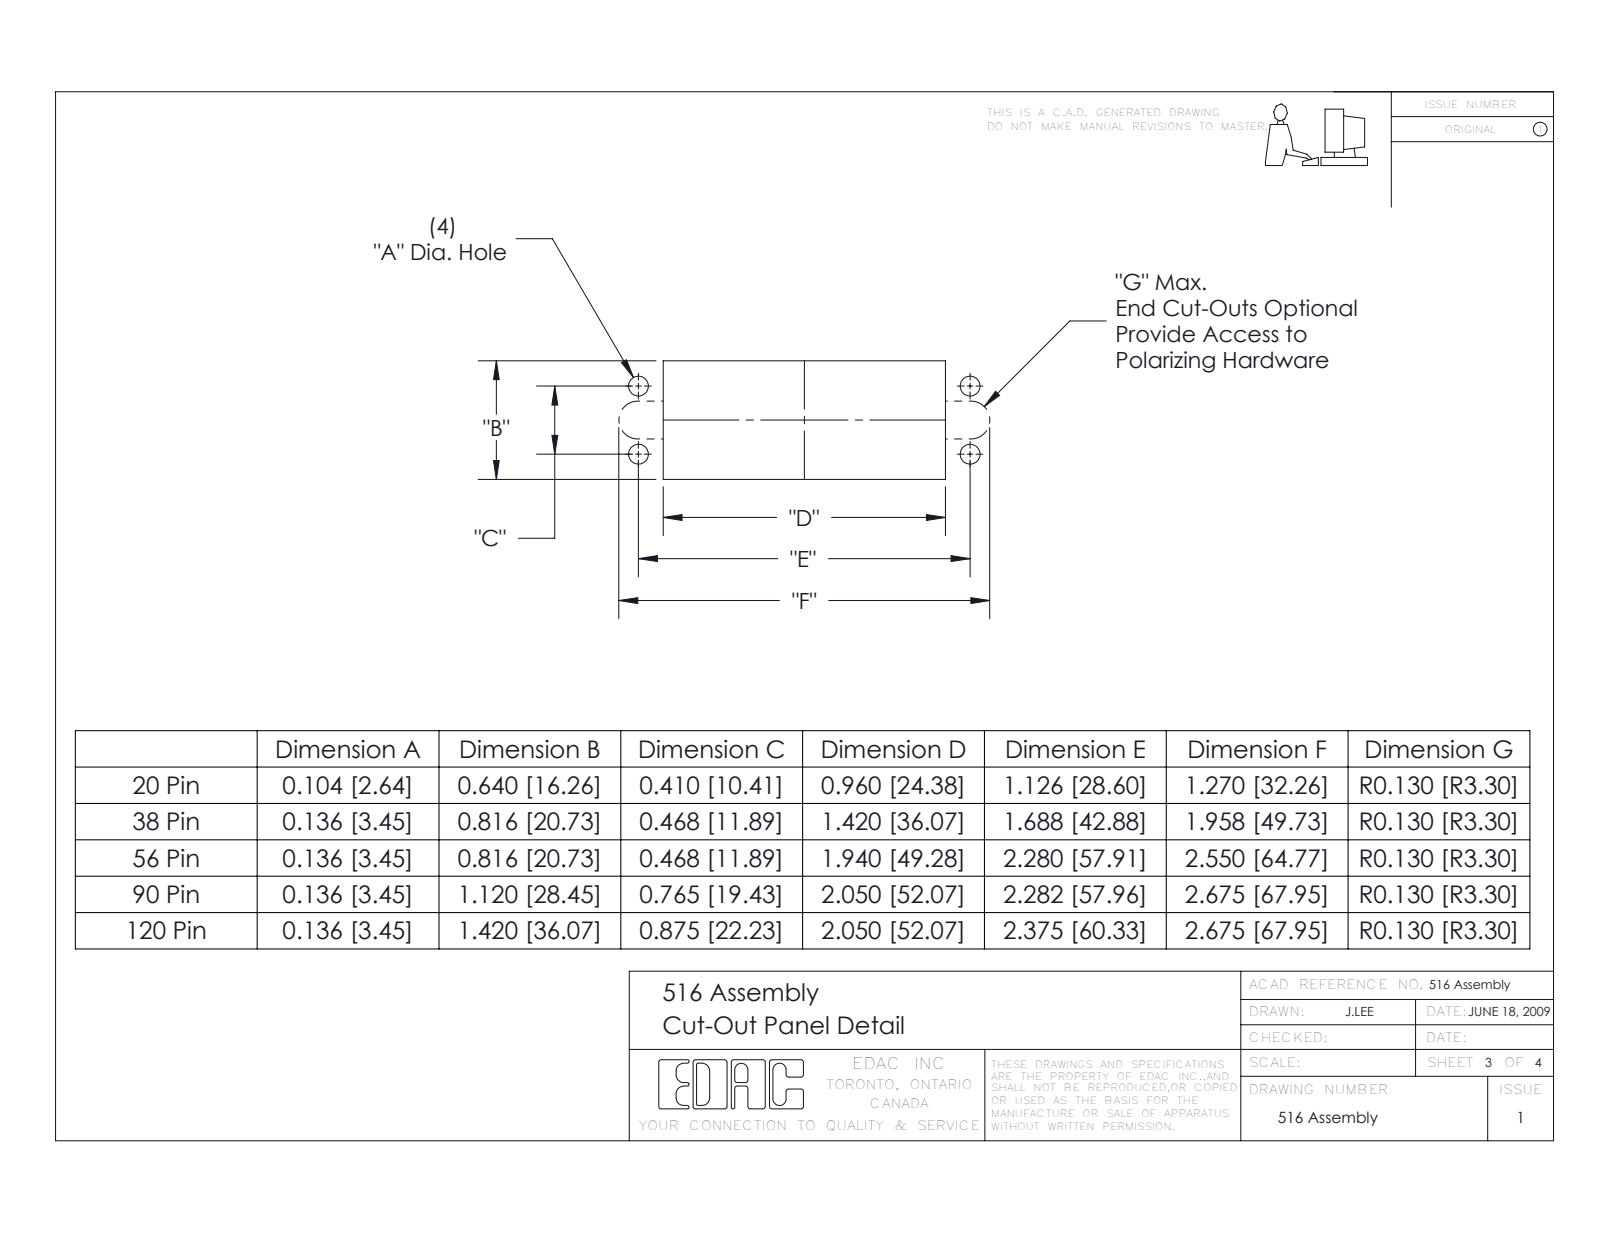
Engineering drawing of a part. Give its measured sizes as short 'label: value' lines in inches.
name: 516-221-020-102_020; 516-230-001_Metal - 020 Top Entry; 516-251-025-100; 516-221-020-102_021 (+8 more)
written by: SolidWorks 2016 (CONFIG_CONTROL_DESIGN)
unit: in
bodies: 11 solids, 3526 faces (571 planar, 847 cylindrical, 2108 other)
size: 2.61 × 1.375 × 0.715
volume: 0.608 in³; area: 25.48 in²
holes: 20× ⌀0.13, 4× ⌀0.093, 2× ⌀0.089, 2× ⌀0.102, 2× ⌀0.12, 1× ⌀0.07, 1× ⌀0.094, 1× ⌀0.1, 1× ⌀0.111, 1× ⌀0.129, 1× ⌀0.172, 1× ⌀0.275
bosses: 2× ⌀0.25, 2× ⌀0.145, 2× ⌀0.112, 2× ⌀0.085, 2× ⌀0.08, 1× ⌀0.187, 1× ⌀0.156, 1× ⌀0.145
rounds: 22× R0.01, 10× R0.039, 9× R0.05, 8× R0.032, 6× R0.007, 6× R0.031, 6× R0.04, 4× R0.078
face distances: 0.05, 0.665, 0.615, 0.715, 1.275, 0.069, 0.15, 0.13, 0.28, 0.057
hole spacings: 0.15, 0.29, 0.15, 0.437, 0.26, 0.359, 0.41, 0.541
